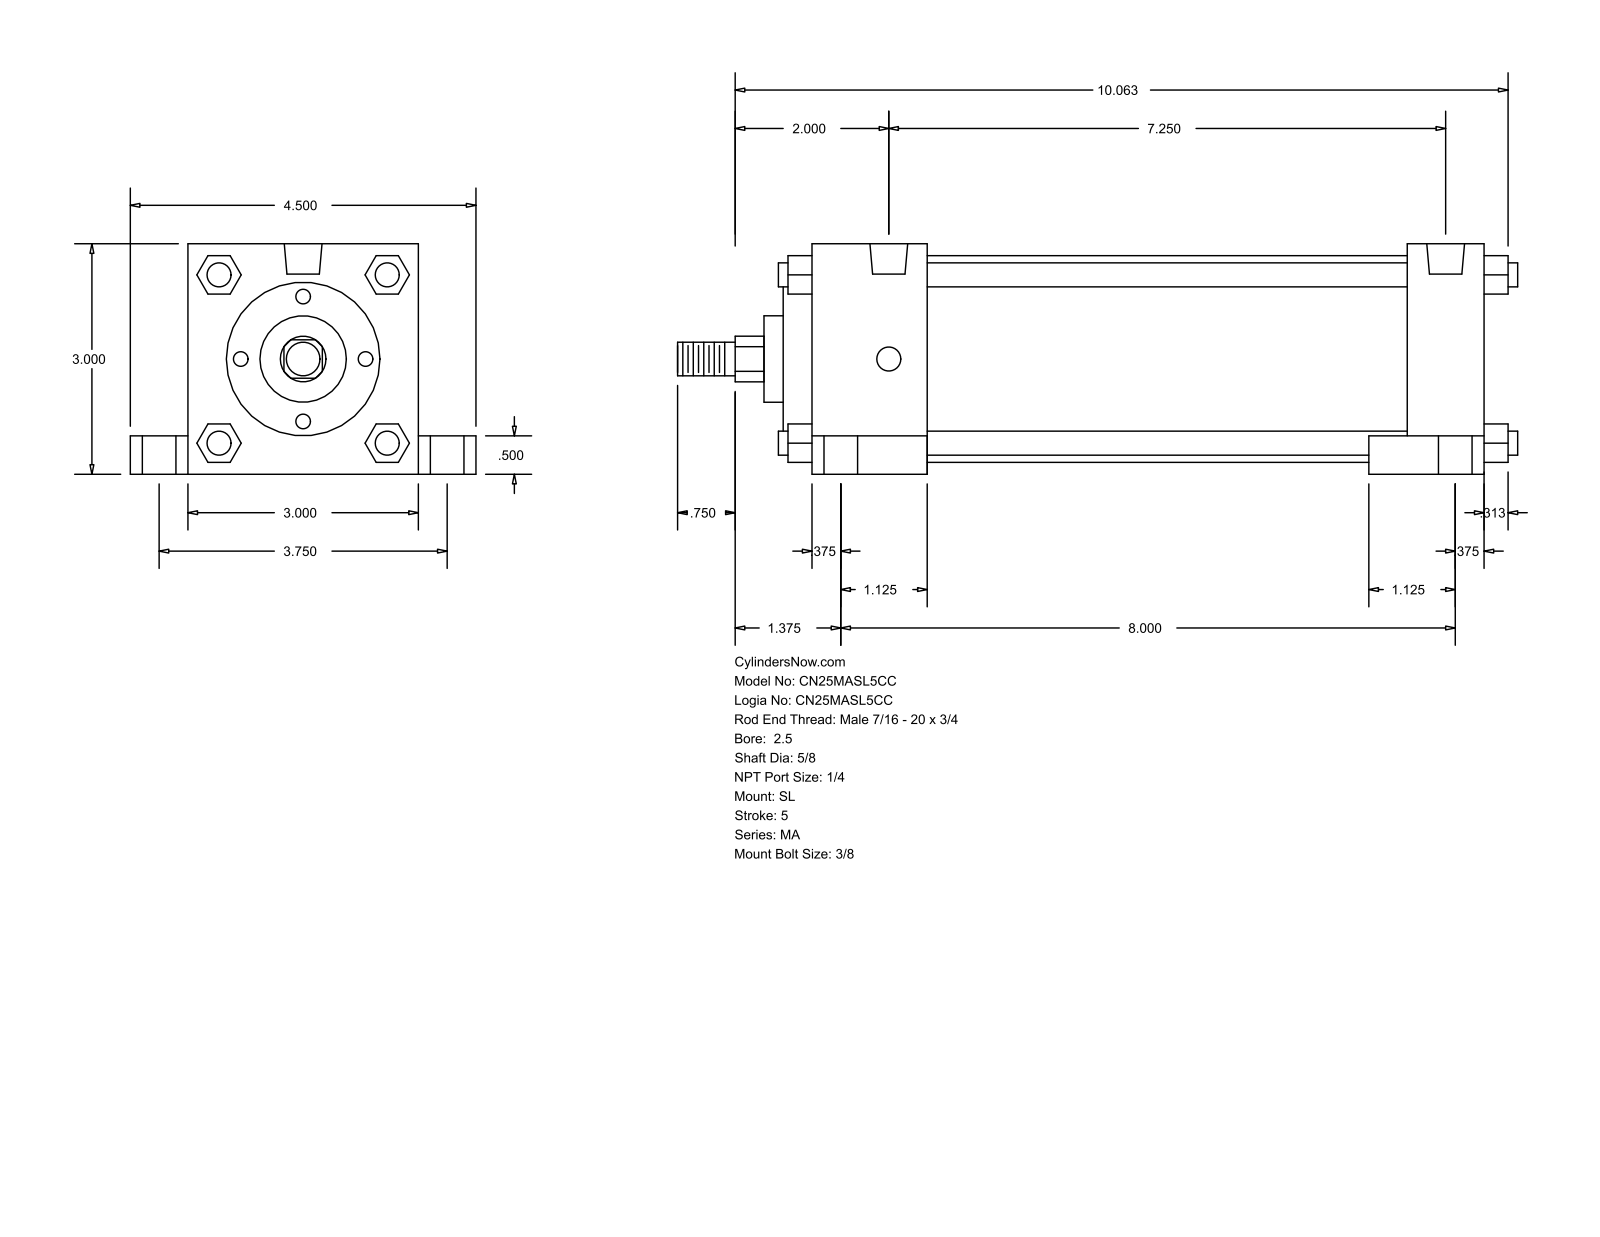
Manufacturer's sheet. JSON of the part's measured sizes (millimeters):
{"part_name": "MA_SL__0250_0.625", "step_written_by": "GSSL Pune (CONFIG_CONTROL_DESIGN)", "units": "millimeters", "bodies": {"solids": 0, "faces": 150, "planar": 113, "cylindrical": 37, "other": 0}, "overall_size": [277.81, 114.3, 76.2], "round_holes": [[7.94, 4], [11.11, 4], [17.46, 4], [12.49, 2]], "round_bosses_or_shafts": [[7.94, 4], [68.33, 1], [50.8, 1], [28.57, 1], [15.88, 1], [11.11, 1]], "partial_cylinders_radius": [[7.54, 1]], "face_to_face_distances": [76.2, 222.25, 12.7, 158.75, 25.4, 38.1, 184.15, 196.85, 19.05, 63.5], "hole_center_spacings": [47.73, 50.2, 95.24, 184.15, 193.28, 203.2, 205.62, 224.41]}
